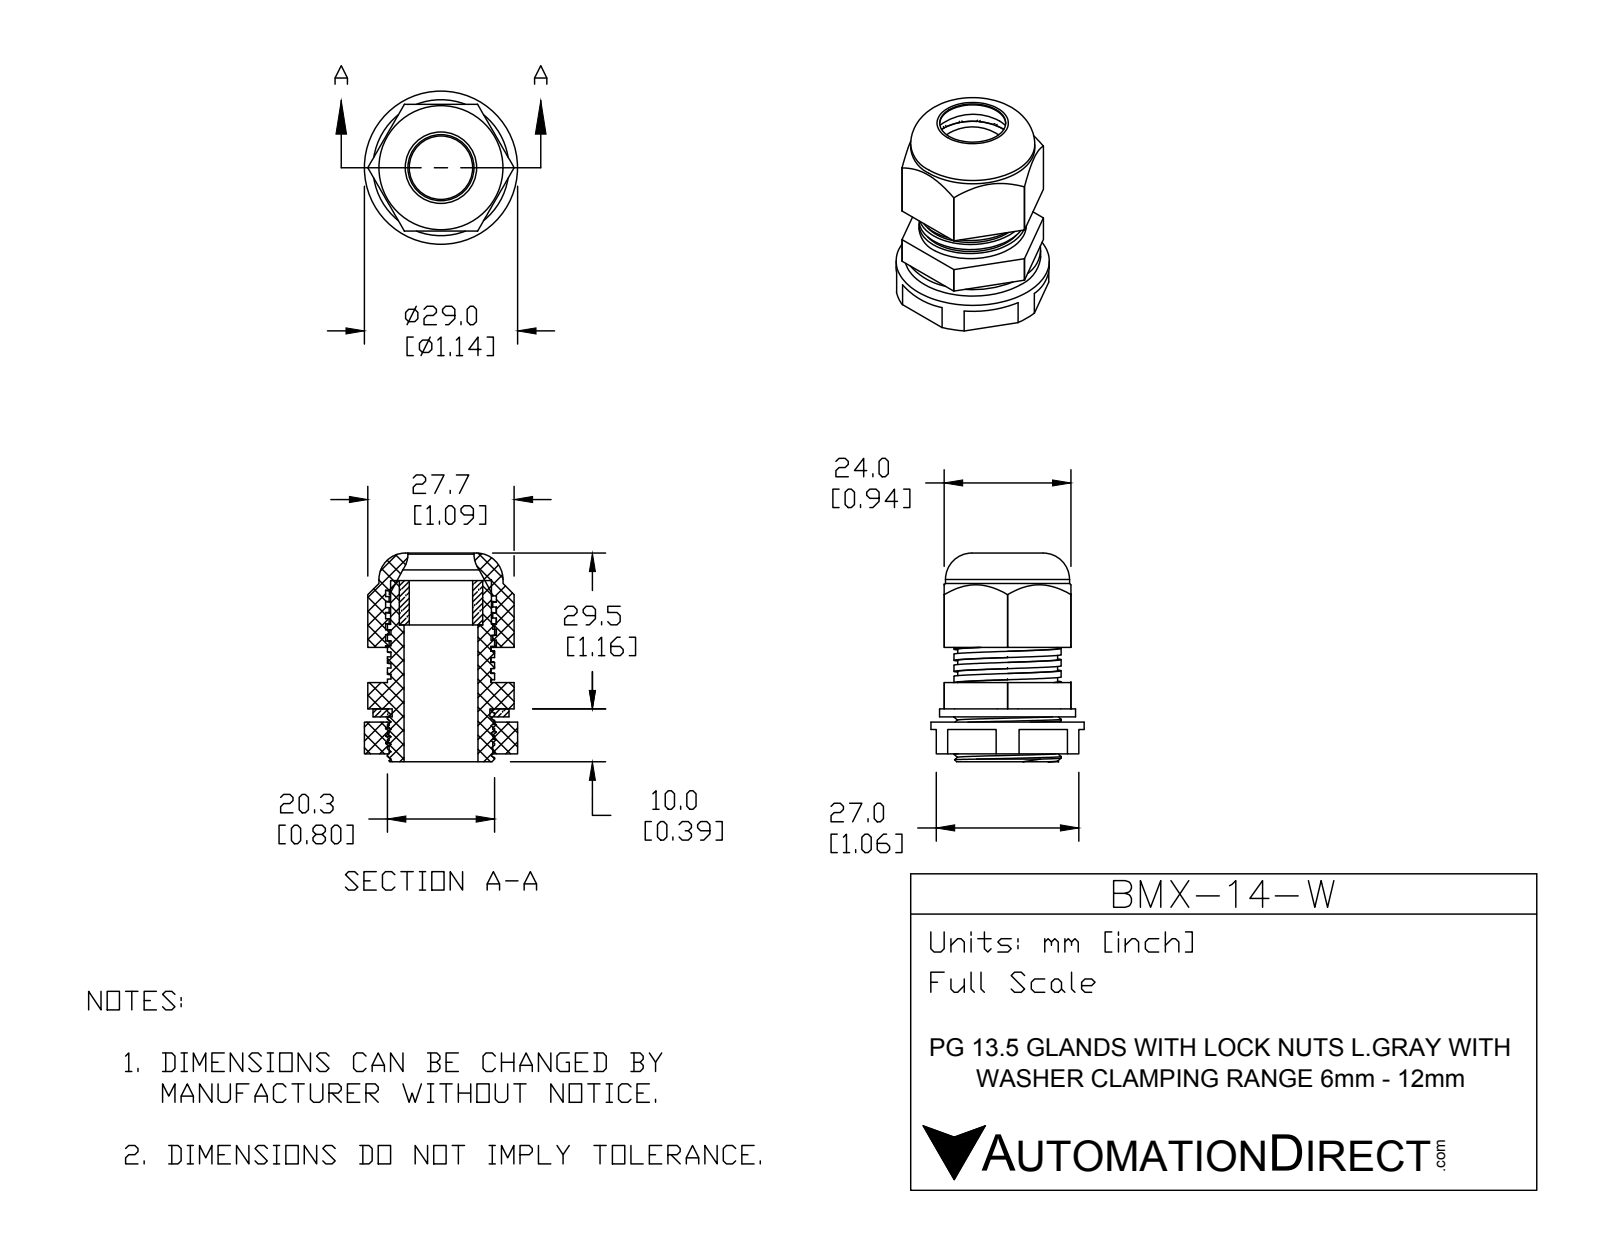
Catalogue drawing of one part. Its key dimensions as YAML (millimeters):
part_name: "BMX-14-W"
step_written_by: "SolidWorks 2015 (CONFIG_CONTROL_DESIGN)"
units: millimeters
bodies: {solids: 5, faces: 200, planar: 100, cylindrical: 78, other: 22}
overall_size: [39.5, 29, 29]
volume: 11926
surface_area: 11980
round_holes:
  - {diameter: 12, count: 1}
  - {diameter: 12.5, count: 1}
  - {diameter: 14, count: 1}
  - {diameter: 15.8, count: 1}
  - {diameter: 18.5, count: 1}
  - {diameter: 19.63, count: 1}
round_bosses_or_shafts:
  - {diameter: 29, count: 1}
  - {diameter: 25.75, count: 1}
  - {diameter: 23.5, count: 1}
  - {diameter: 20.3, count: 1}
  - {diameter: 19.1, count: 1}
partial_cylinders:
  - {radius: 13.85, count: 1}
face_to_face_distances: [1.5, 24, 8.5, 2.5, 7.5, 6, 25.5, 7, 1, 13.5]
